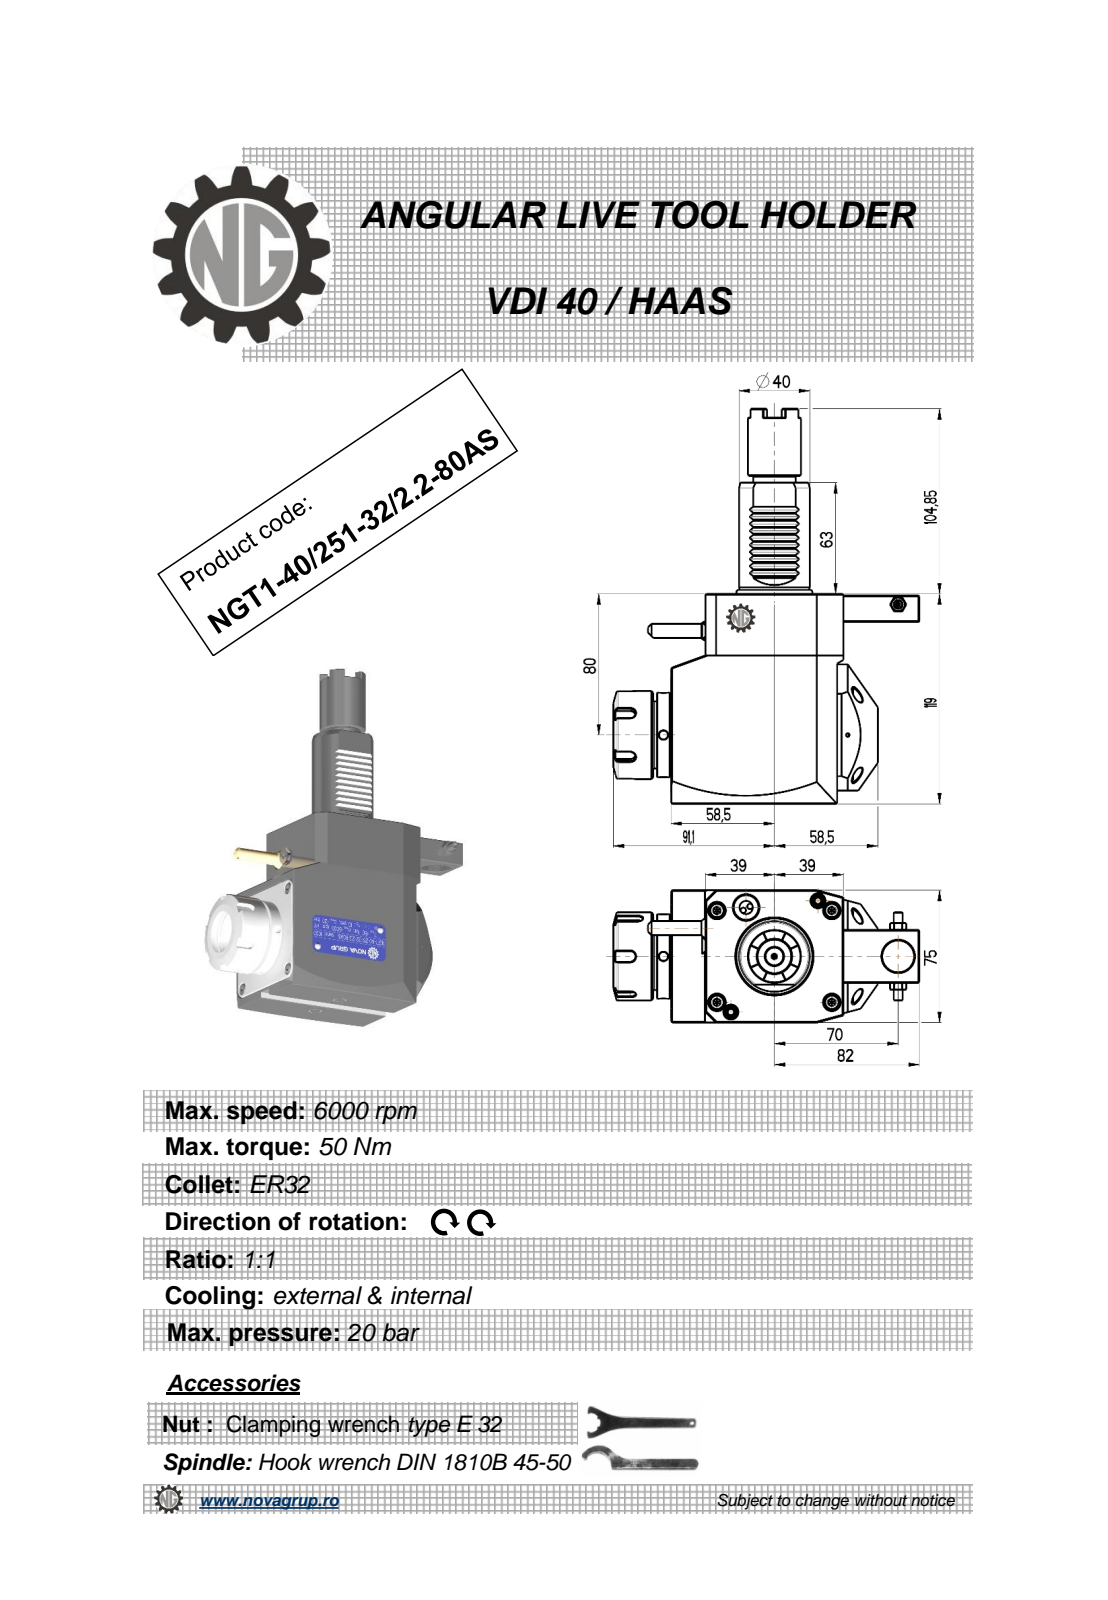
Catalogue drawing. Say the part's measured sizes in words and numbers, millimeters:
The part is named "NGT1_40_251_32_2_2_80AS". Its 3-D file was written by "PRO/ENGINEER BY PARAMETRIC TECHNOLOGY CORPORATION, 2010280 (CONFIG_CONTROL_DESIGN)". It is 1 solid with 475 faces: 236 planar, 100 cylindrical and 139 other. Overall it measures 223.85 by 173.1 by 76.6 millimeters. Its volume is 1 021 000 cubic millimeters and its surface area 81 934 square millimeters. Round holes: 3 of diameter 5, 1 of diameter 3, 1 of diameter 4.2, 1 of diameter 9.5, 1 of diameter 18, 1 of diameter 27. Round bosses or shafts: 1 of diameter 50, 1 of diameter 48, 1 of diameter 41.5, 1 of diameter 41, 1 of diameter 40, 1 of diameter 30, 1 of diameter 24, 1 of diameter 10. Partial cylindrical surfaces (rounded edges, fillets, slot ends): 12 of radius 0.26, 10 of radius 0.3, 6 of radius 0.2, 5 of radius 3, 2 of radius 5.8, 2 of radius 6, 2 of radius 600, 1 of radius 0.5. The main face-to-face distances are 75, 119, 19.5, 97.5, 78, 1, 3.5, 22.5, 19.3, 97.3. The hole center spacings are 20.93, 61.13, 72.5, 132.75, 151.98.
